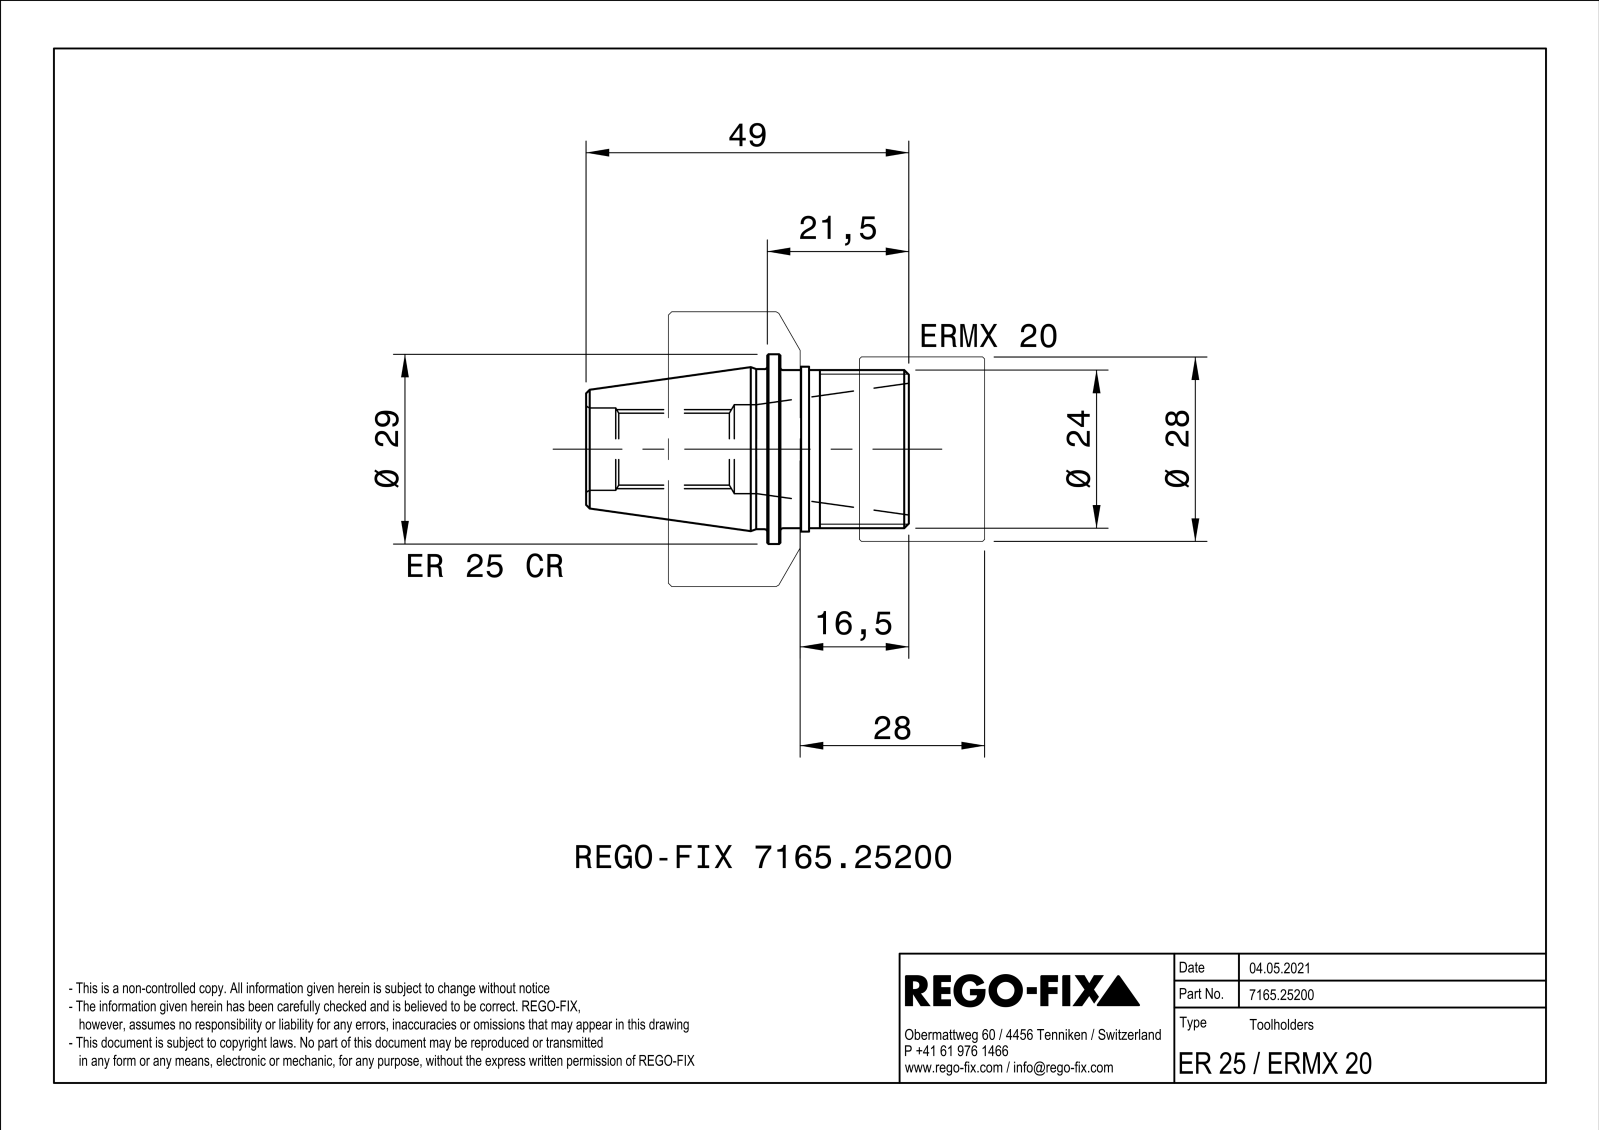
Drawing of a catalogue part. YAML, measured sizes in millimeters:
part_name: "NOCUT"
step_written_by: "SIEMENS PLM Software Solid Edge ST10 (AUTOMOTIVE_DESIGN)"
units: millimeters
bodies: {solids: 1, faces: 118, planar: 61, cylindrical: 17, other: 40}
overall_size: [49, 41.7, 41.7]
volume: 21790
surface_area: 11888
round_holes:
  - {diameter: 10.92, count: 1}
  - {diameter: 12.5, count: 1}
  - {diameter: 13.5, count: 1}
  - {diameter: 24.4, count: 1}
  - {diameter: 30.38, count: 1}
  - {diameter: 32.5, count: 1}
round_bosses_or_shafts:
  - {diameter: 41.7, count: 1}
  - {diameter: 28.9, count: 1}
  - {diameter: 28.8, count: 1}
  - {diameter: 24.3, count: 1}
  - {diameter: 24, count: 1}
  - {diameter: 22.4, count: 1}
  - {diameter: 10, count: 1}
partial_cylinders:
  - {radius: 6, count: 2}
face_to_face_distances: [16, 1.35, 17.35, 1.2, 16.15, 16.5, 32.5, 4.35, 3.15, 3]
